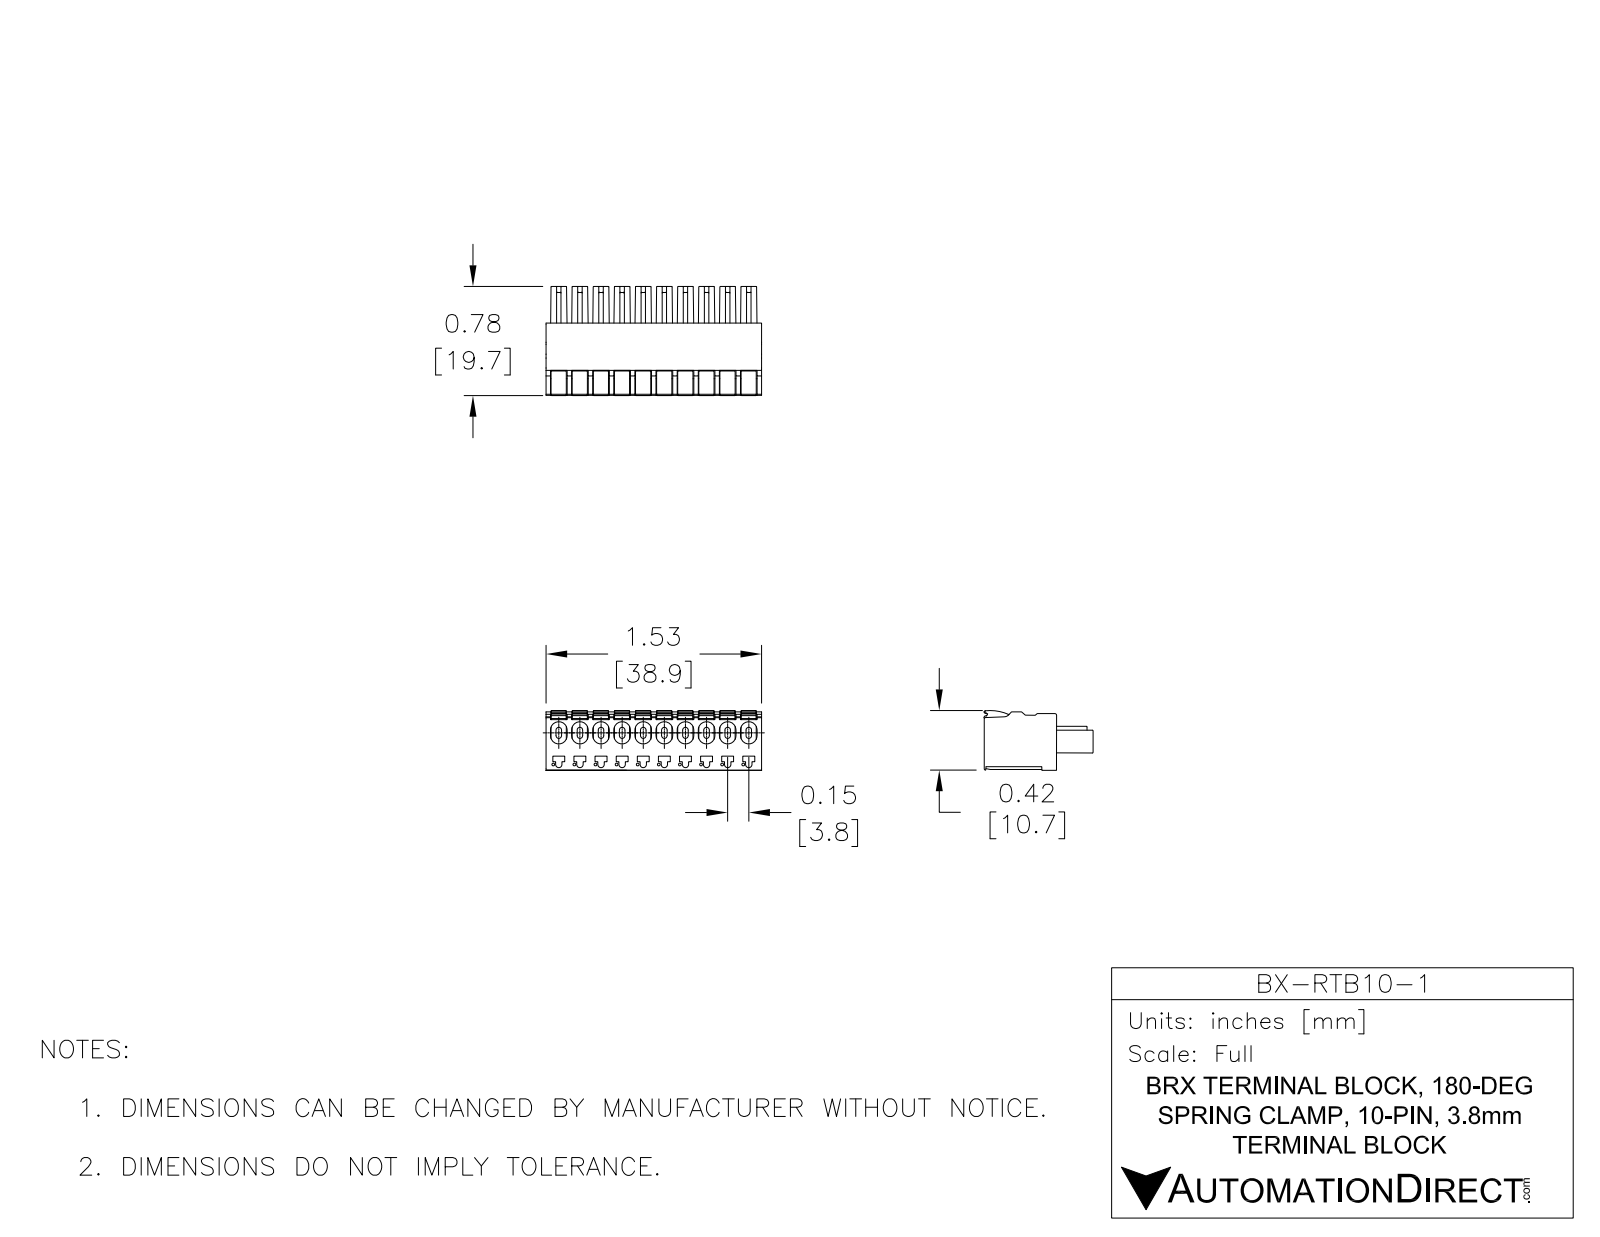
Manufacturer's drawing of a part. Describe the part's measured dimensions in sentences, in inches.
The part is named "BX-RTB10-1". Its 3-D file was written by "SolidWorks 2016 (AUTOMOTIVE_DESIGN)". It is 11 solids with 1431 faces: 485 planar, 598 cylindrical and 348 other. Overall it measures 1.531 by 0.776 by 0.425 inches. Its volume is 0.316 cubic inches and its surface area 8.088 square inches. Round holes: 10 of diameter 0.02, 10 of diameter 0.063. Partial cylindrical surfaces (rounded edges, fillets, slot ends): 289 of radius 0.004, 20 of radius 0.012, 20 of radius 0.02, 20 of radius 0.059, 10 of radius 0.022, 10 of radius 0.072, 5 of radius 0.008, 2 of radius 0.012. The main face-to-face distances are 0.15, 0.3, 0.45, 0.6, 0.75, 0.118, 0.9, 0.26, 0.514, 1.05. The hole center spacings are 0.15, 0.3, 0.45, 0.6, 0.174, 0.75, 0.202, 0.254.
